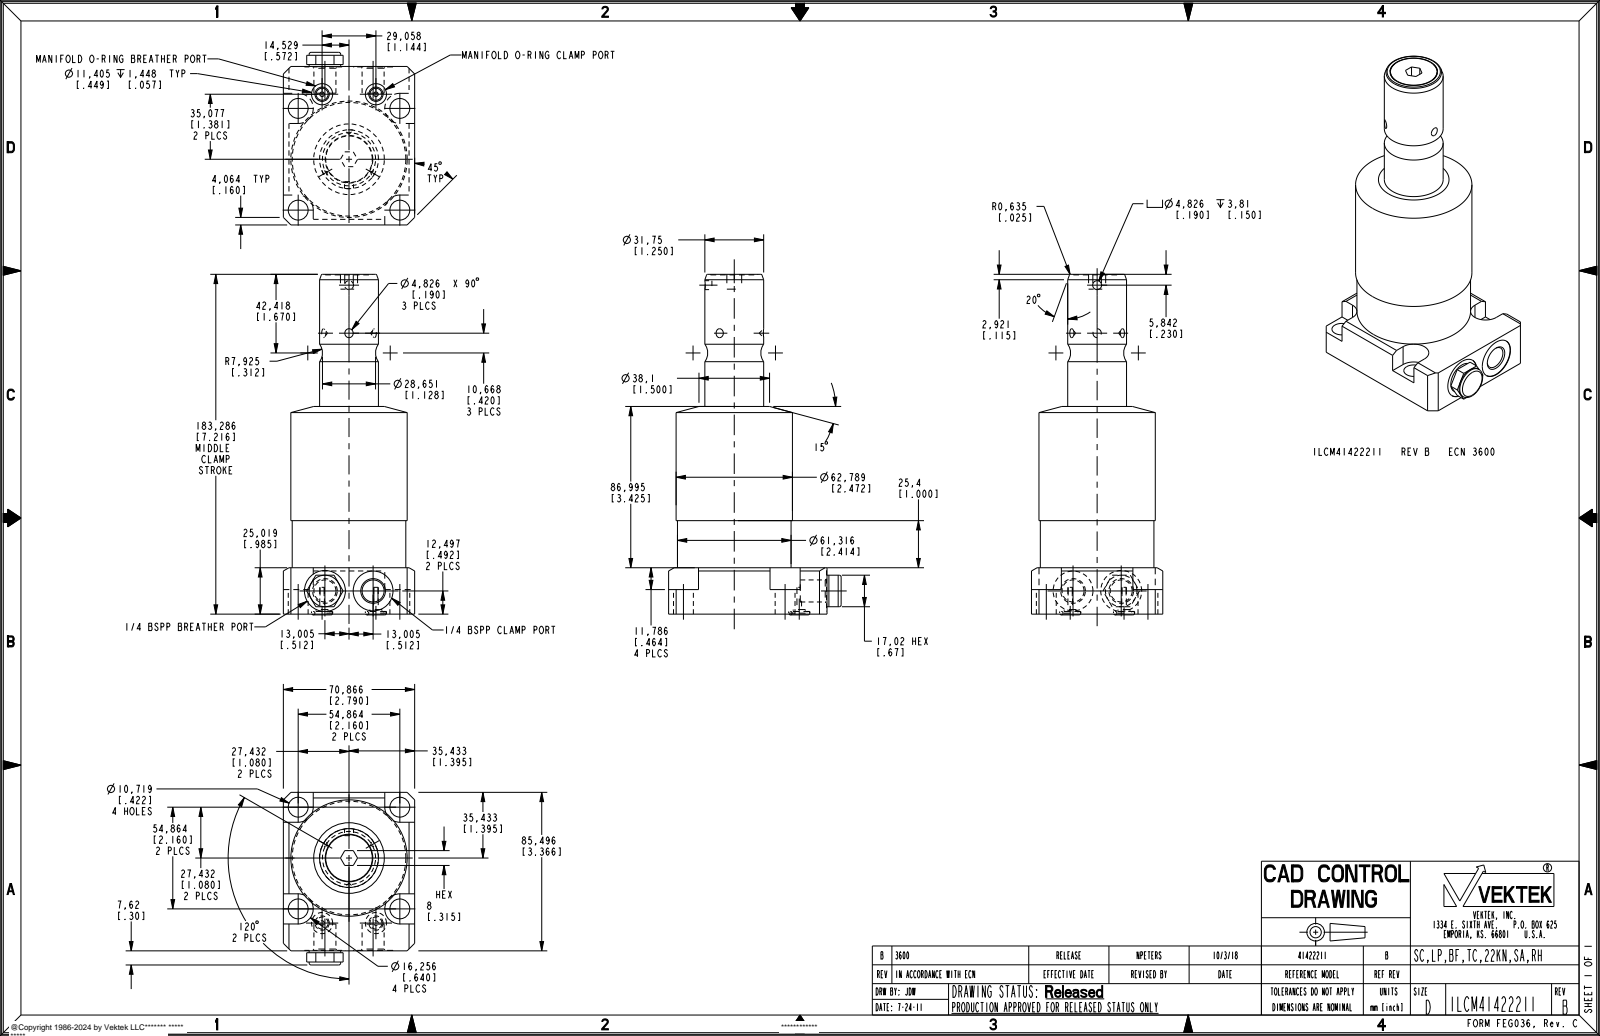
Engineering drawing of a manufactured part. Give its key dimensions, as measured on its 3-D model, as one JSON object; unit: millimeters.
{"part_name": "ILCM41422211", "step_written_by": "PRO/ENGINEER BY PARAMETRIC TECHNOLOGY CORPORATION, 2013320 (AUTOMOTIVE_DESIGN)", "units": "millimeters", "bodies": {"solids": 1, "faces": 153, "planar": 73, "cylindrical": 52, "other": 28}, "overall_size": [183.69, 93.12, 70.87], "volume_mm3": 449732, "surface_area_mm2": 47579, "round_holes": [[10.72, 4], [2.49, 2], [6.5, 2], [11.4, 2], [11.89, 2], [4.83, 1], [21.49, 1], [22.1, 1], [25.65, 1]], "round_bosses_or_shafts": [[62.79, 1], [61.32, 1], [31.75, 1], [25.15, 1], [17.02, 1]], "partial_cylinders_radius": [[8.13, 4]], "face_to_face_distances": [25.02, 70.86, 85.49, 11.79, 13.23, 158.27, 170.06, 183.29, 85.24, 54.73], "hole_center_spacings": [38.79, 54.86, 15, 37.97, 42.65, 63.83, 75.29, 77.58]}
